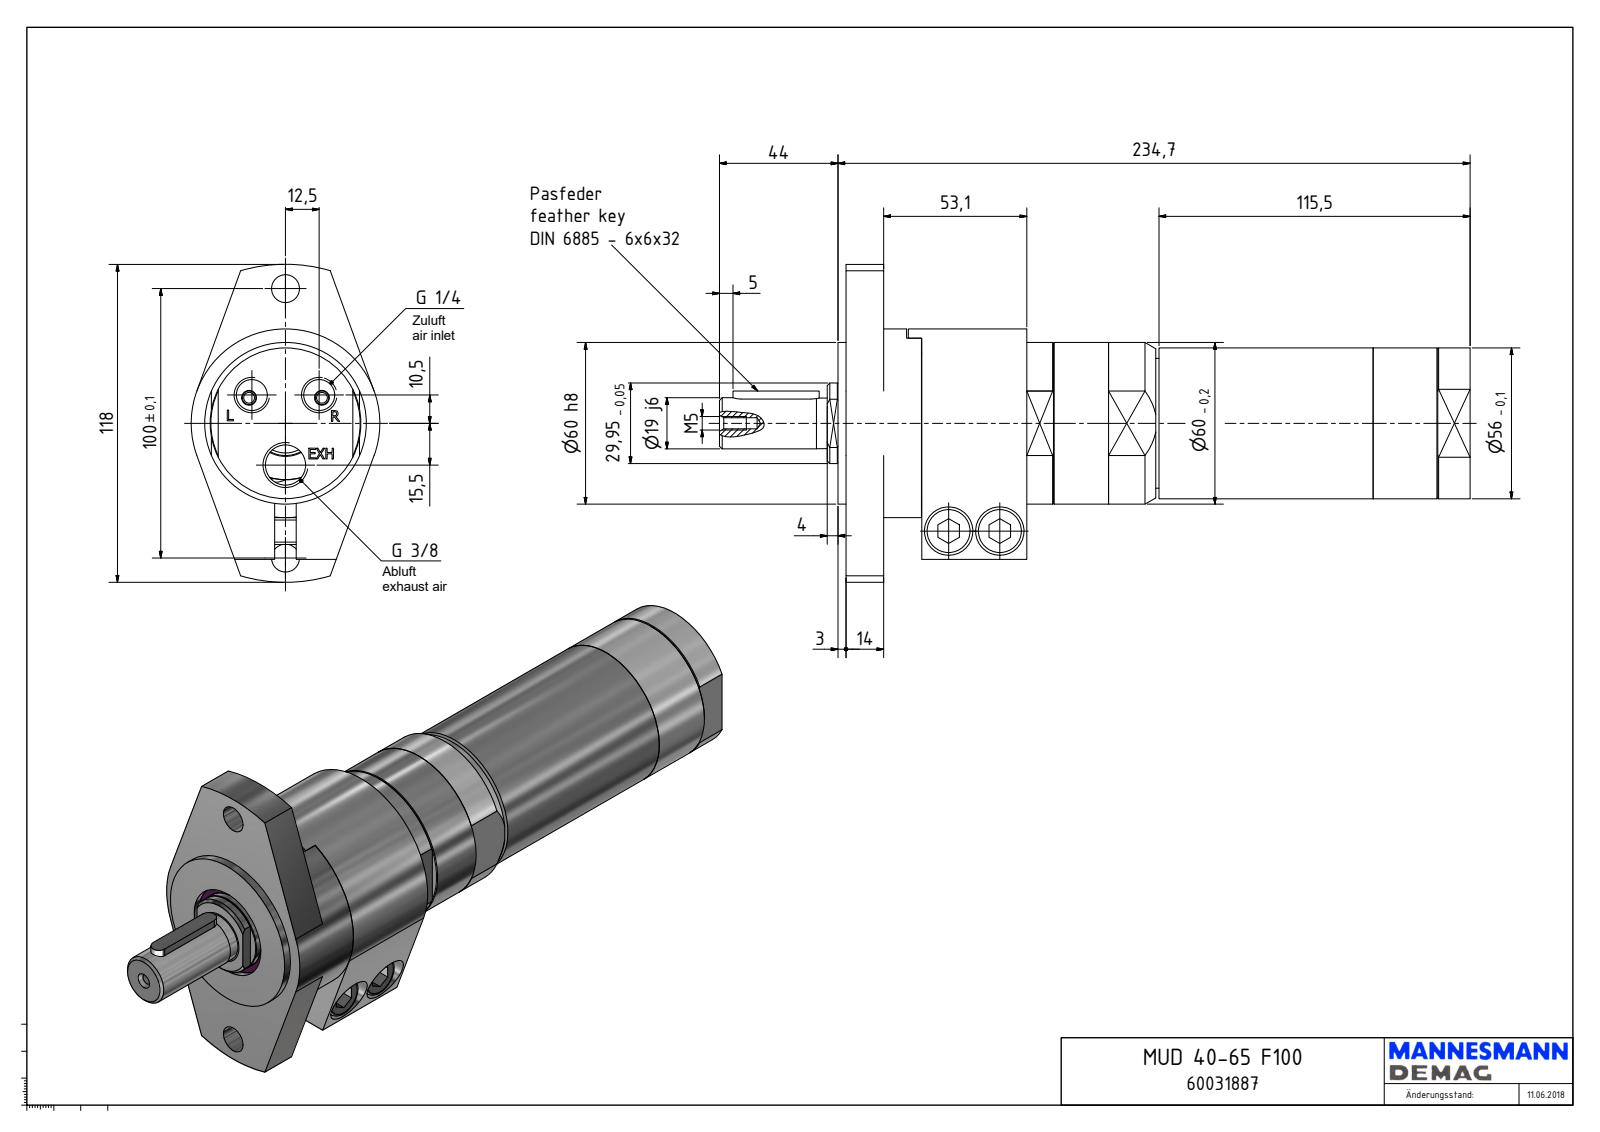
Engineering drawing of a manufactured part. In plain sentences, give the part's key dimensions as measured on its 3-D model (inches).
The part is named "MUD 40-65 F100_60031887". Its 3-D file was written by "Autodesk Inventor 2018 (AUTOMOTIVE_DESIGN)". It is 1 solid with 297 faces: 165 planar, 75 cylindrical and 57 other. Overall it measures 10.972 by 4.646 by 2.756 inches. Its volume is 45.62 cubic inches and its surface area 129.6 square inches. Round holes: 2 of diameter 0.33, 2 of diameter 0.406, 2 of diameter 0.413, 2 of diameter 0.451, 2 of diameter 0.709, 1 of diameter 0.061, 1 of diameter 0.157, 1 of diameter 0.163, 1 of diameter 0.217, 1 of diameter 0.589, 1 of diameter 1.378, 1 of diameter 1.437. Round bosses or shafts: 2 of diameter 0.63, 2 of diameter 0.394, 1 of diameter 2.756, 1 of diameter 2.362, 1 of diameter 2.205, 1 of diameter 2.172, 1 of diameter 1.897, 1 of diameter 1.179. Partial cylindrical surfaces (rounded edges, fillets, slot ends): 6 of radius 0.394, 2 of radius 0.118, 2 of radius 0.236, 1 of radius 0.766, 1 of radius 0.881, 1 of radius 0.906, 1 of radius 1.031, 1 of radius 2.323. The main face-to-face distances are 0.551, 0.669, 0.118, 2.76, 9.24, 9.122, 8.571, 2.642, 2.091, 6.48. The hole center spacings are 0.643, 1.136, 1.631, 1.969, 2.432, 0.61, 0.748, 0.984.
